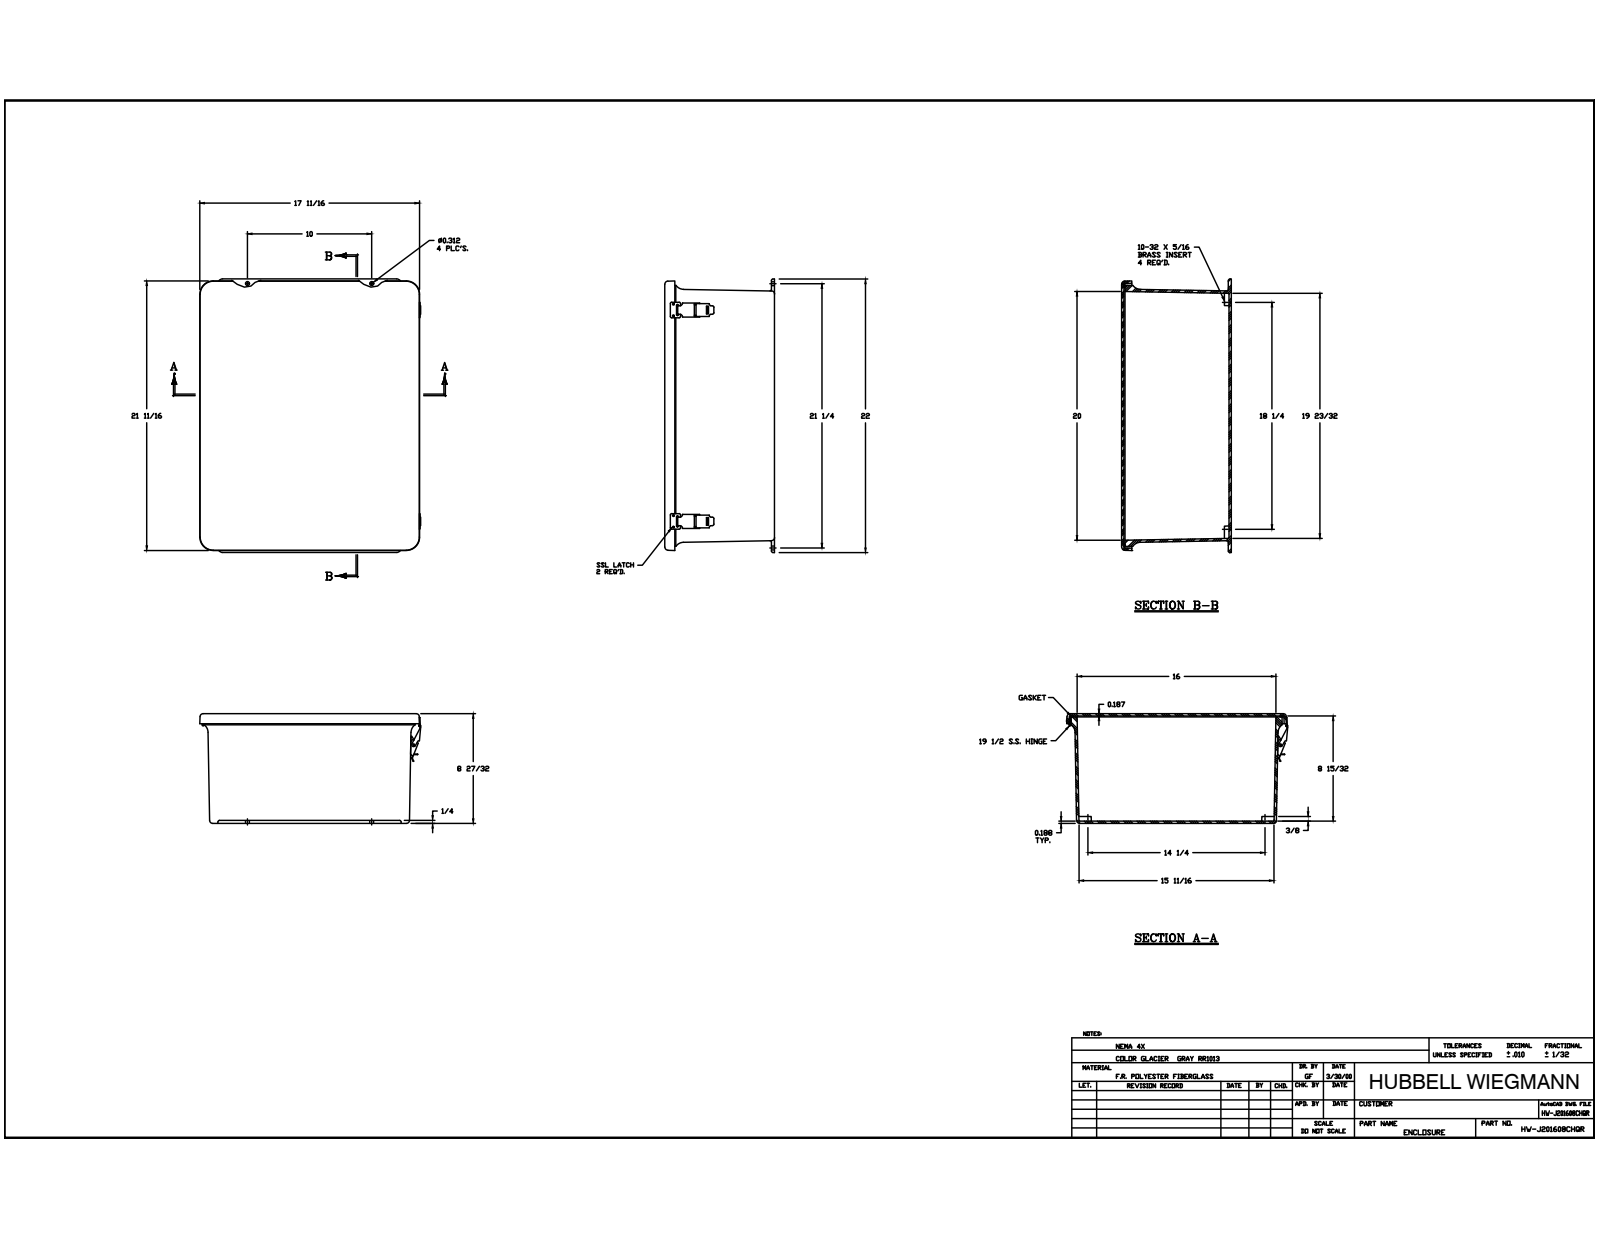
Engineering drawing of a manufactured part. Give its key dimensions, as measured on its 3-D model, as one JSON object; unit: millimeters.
{"part_name": "J2016HL_2; RMINS45821P_19; RMINS45821P_20; RMINS45821P_21 (+8 more)", "step_written_by": "Autodesk Inventor 2014 (AUTOMOTIVE_DESIGN)", "units": "millimeters", "bodies": {"solids": 42, "faces": 1165, "planar": 533, "cylindrical": 489, "other": 143}, "overall_size": [558.8, 451.39, 224.26], "volume_mm3": 4647000, "surface_area_mm2": 1917000, "round_holes": [[3.56, 24], [3.33, 12], [2.64, 8], [3.86, 5], [3.3, 4], [3.96, 4], [5.54, 4], [3.43, 3], [9.52, 2], [2.16, 1]], "round_bosses_or_shafts": [[3.17, 20], [6.35, 12], [6.86, 4], [7.62, 2], [4.31, 1], [3.94, 1], [3.05, 1]], "partial_cylinders_radius": [[0.38, 20], [0.79, 20], [3.17, 18], [1.14, 16], [0.76, 12], [0.57, 9], [6.35, 8], [1.52, 6]], "face_to_face_distances": [4.76, 219.5, 224.26, 4.77, 214.73, 219.49, 7.94, 12.7, 217.49, 212.72], "hole_center_spacings": [431.8, 95.25, 190.5, 6.35, 23.81, 432.22, 88.9, 101.6]}
